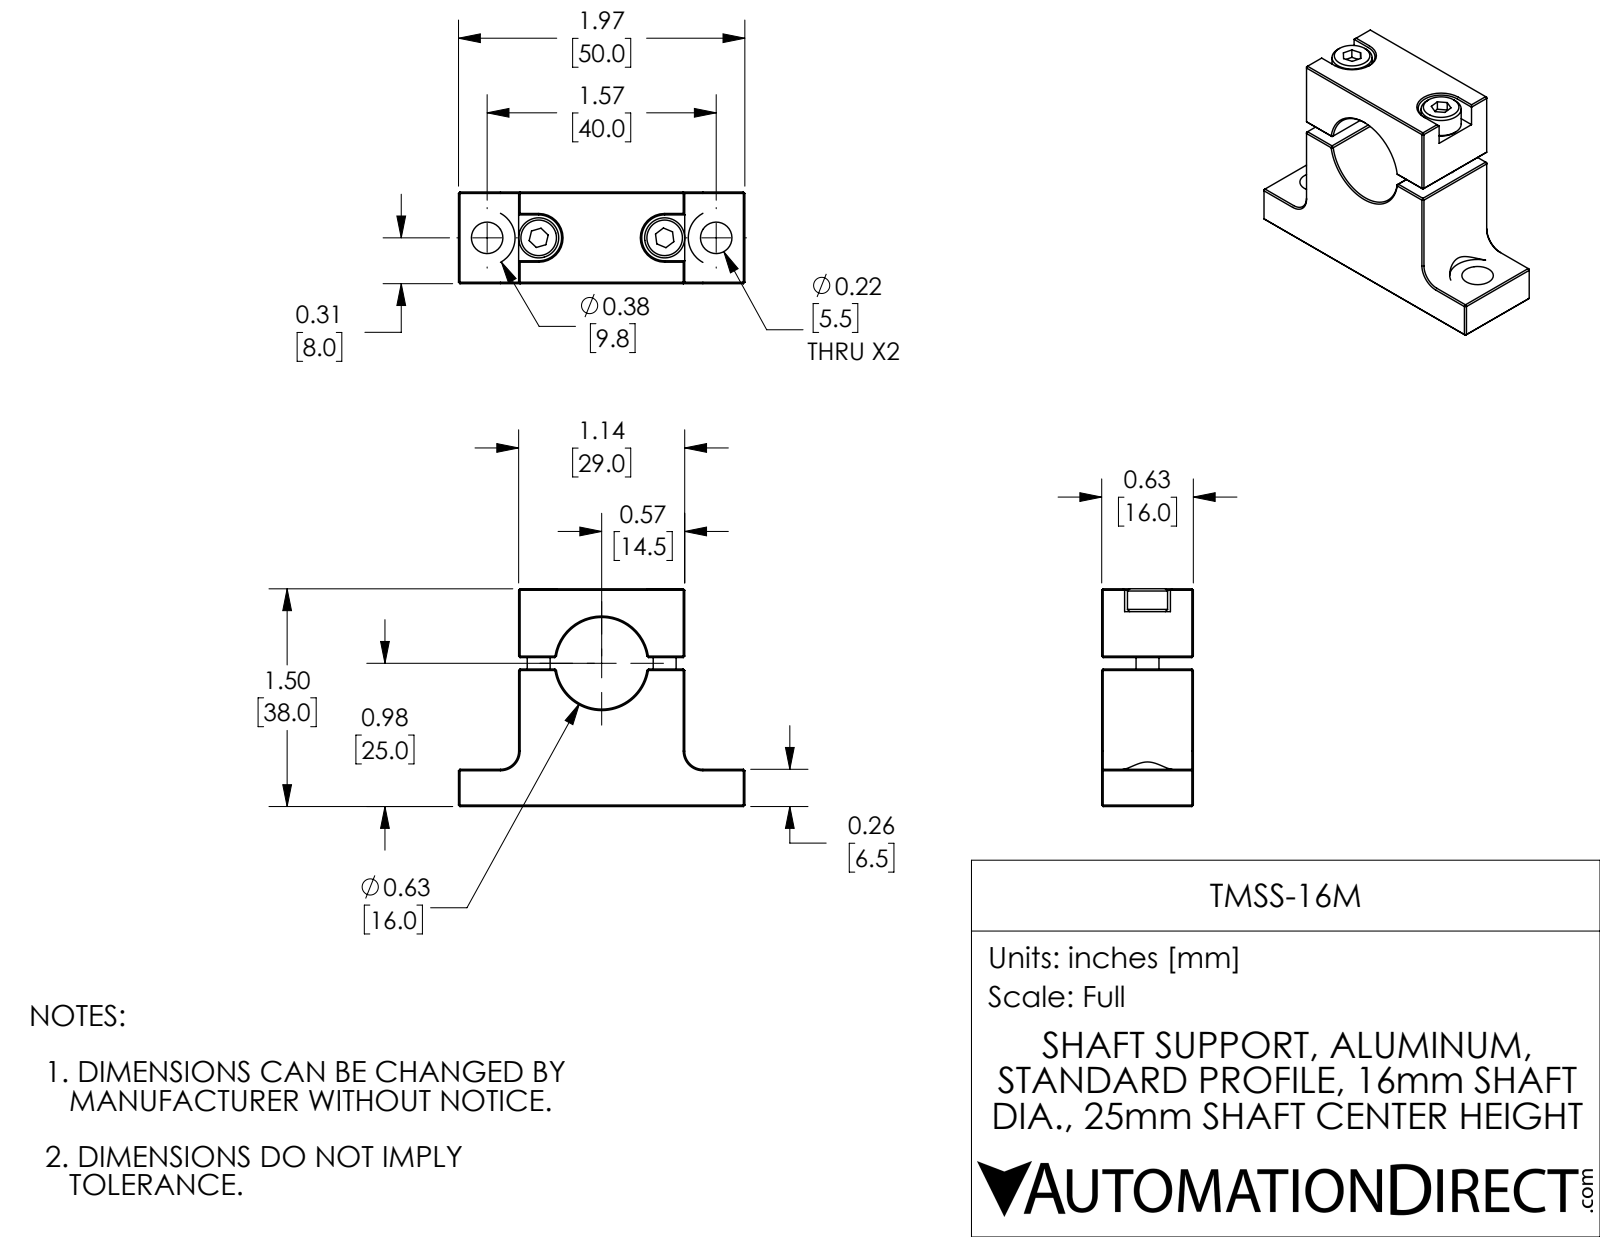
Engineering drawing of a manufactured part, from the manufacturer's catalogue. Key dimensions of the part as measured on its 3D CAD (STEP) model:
Part name (STEP PRODUCT): TMSS-16M
STEP written by: SolidWorks 2017 (AUTOMOTIVE_DESIGN)
Units: inches
Bodies: 4 solids, 176 faces (120 planar, 32 cylindrical, 24 other)
Overall size (bounding box): 1.969 × 1.497 × 0.63
Volume: 0.946 in³ · Surface area: 11.46 in²
Round holes (diameter × count): ⌀0.128 ×2, ⌀0.177 ×2, ⌀0.217 ×2, ⌀0.094 ×1, ⌀0.63 ×1
Round bosses / shafts (diameter × count): ⌀0.276 ×2, ⌀0.157 ×2
Partial cylindrical surfaces — rounded edges, fillets, slot ends (radius × count): R0.125 ×2, R0.192 ×2, R0.157 ×1, R0.158 ×1
Main face-to-face distances: 0.63, 1.142, 1.496, 0.472, 0.256, 1.24, 0.413, 1.555, 0.945, 0.689
Hole centre spacings: 0.354, 0.433, 0.787, 1.22, 0.866, 1.575
